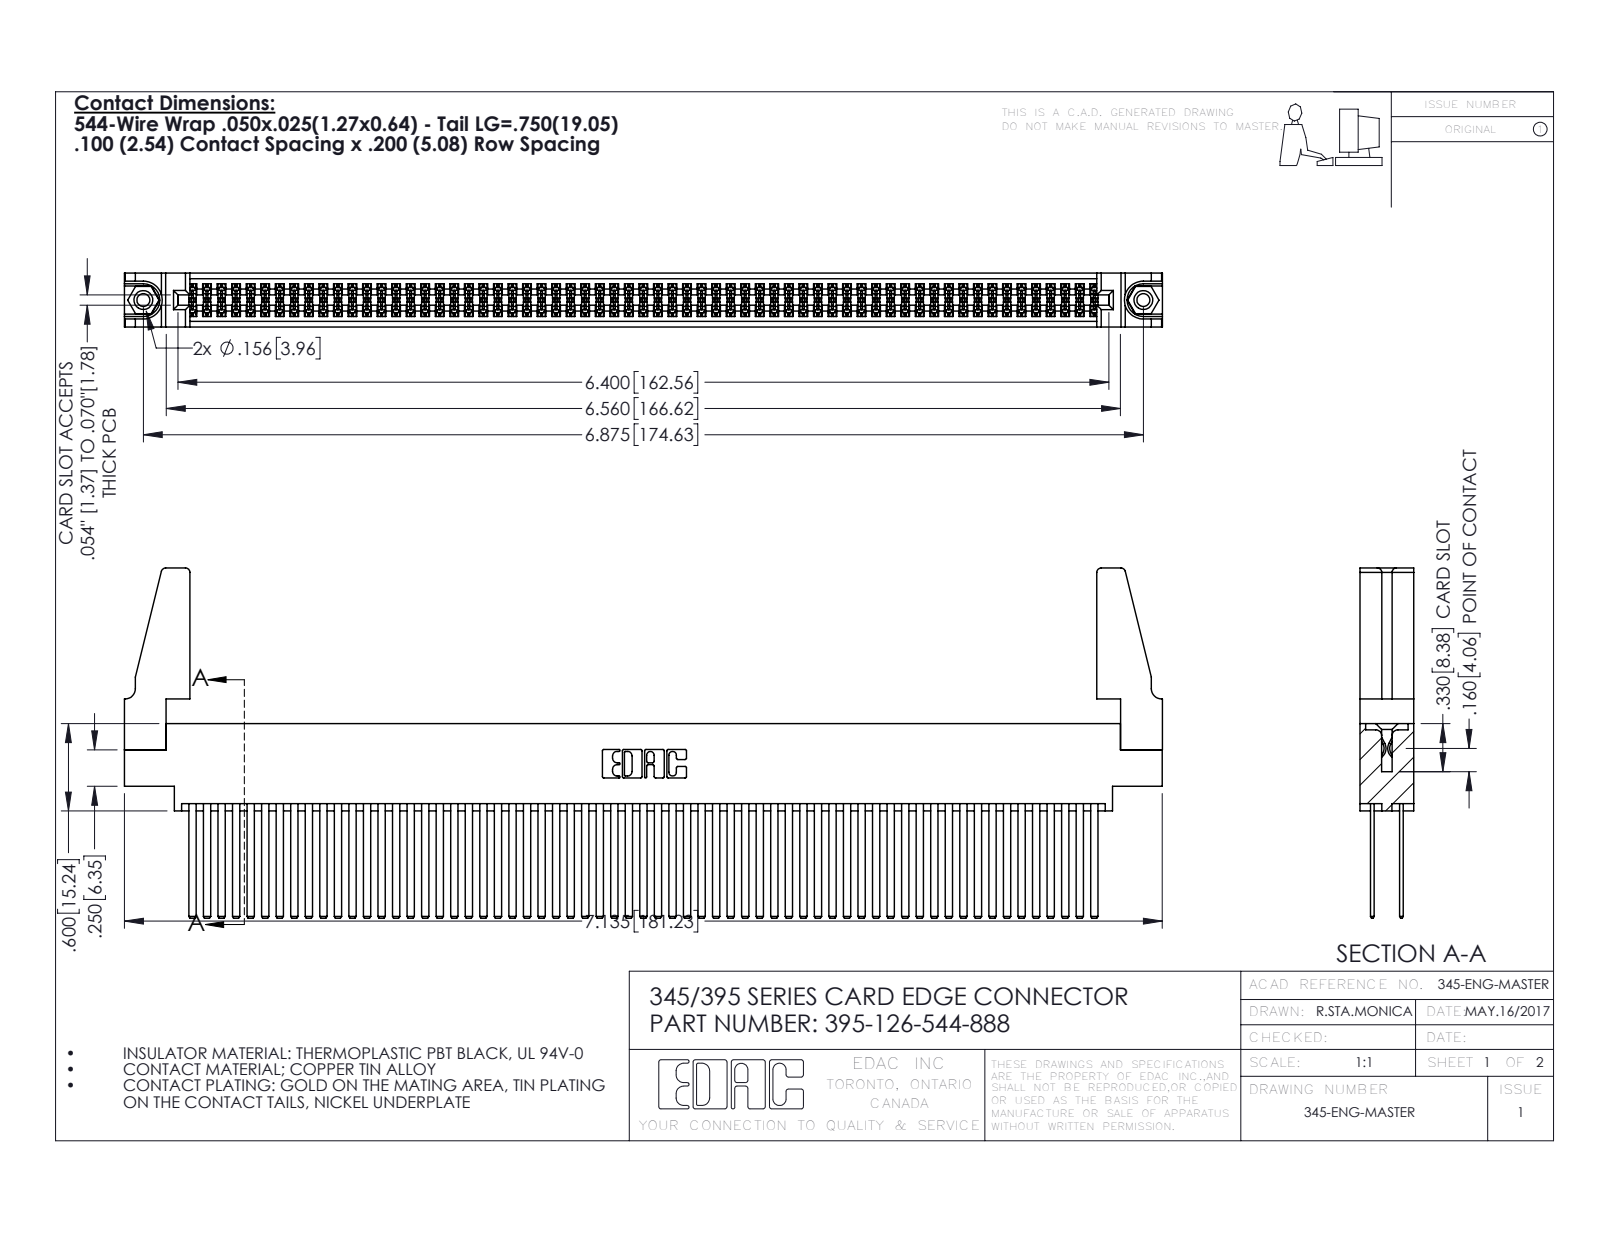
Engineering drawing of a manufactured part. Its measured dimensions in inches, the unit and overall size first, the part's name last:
Units: inches
Overall size (bounding box): 7.136 × 2.407 × 0.37
Round holes (diameter × count): ⌀0.089 ×2, ⌀0.125 ×2, ⌀0.156 ×2, ⌀0.064 ×1
Round bosses / shafts (diameter × count): ⌀0.155 ×2
Partial cylindrical surfaces — rounded edges, fillets, slot ends (radius × count): R0.006 ×189, R0.01 ×22, R0.03 ×8, R0.007 ×6, R0.031 ×6, R0.026 ×3, R0.014 ×2, R0.019 ×2
Main face-to-face distances: 0.072, 0.298, 0.2, 0.098, 0.272, 0.025, 0.225, 0.37, 0.175, 0.149
Hole centre spacings: 0.27, 6.639, 6.875
Volume: 1.386 in³ · Surface area: 58.29 in²
Bodies: 131 solids, 5798 faces (3810 planar, 1972 cylindrical, 16 other)
Part name (STEP PRODUCT): 395-126-544-888; 345-292-001_345-293-144; 345-250-001_345-250-001-102; 345 Part_0.170 Offset - 0.156 Dia-TH (+1 more)
STEP written by: SolidWorks 2016 (CONFIG_CONTROL_DESIGN)
